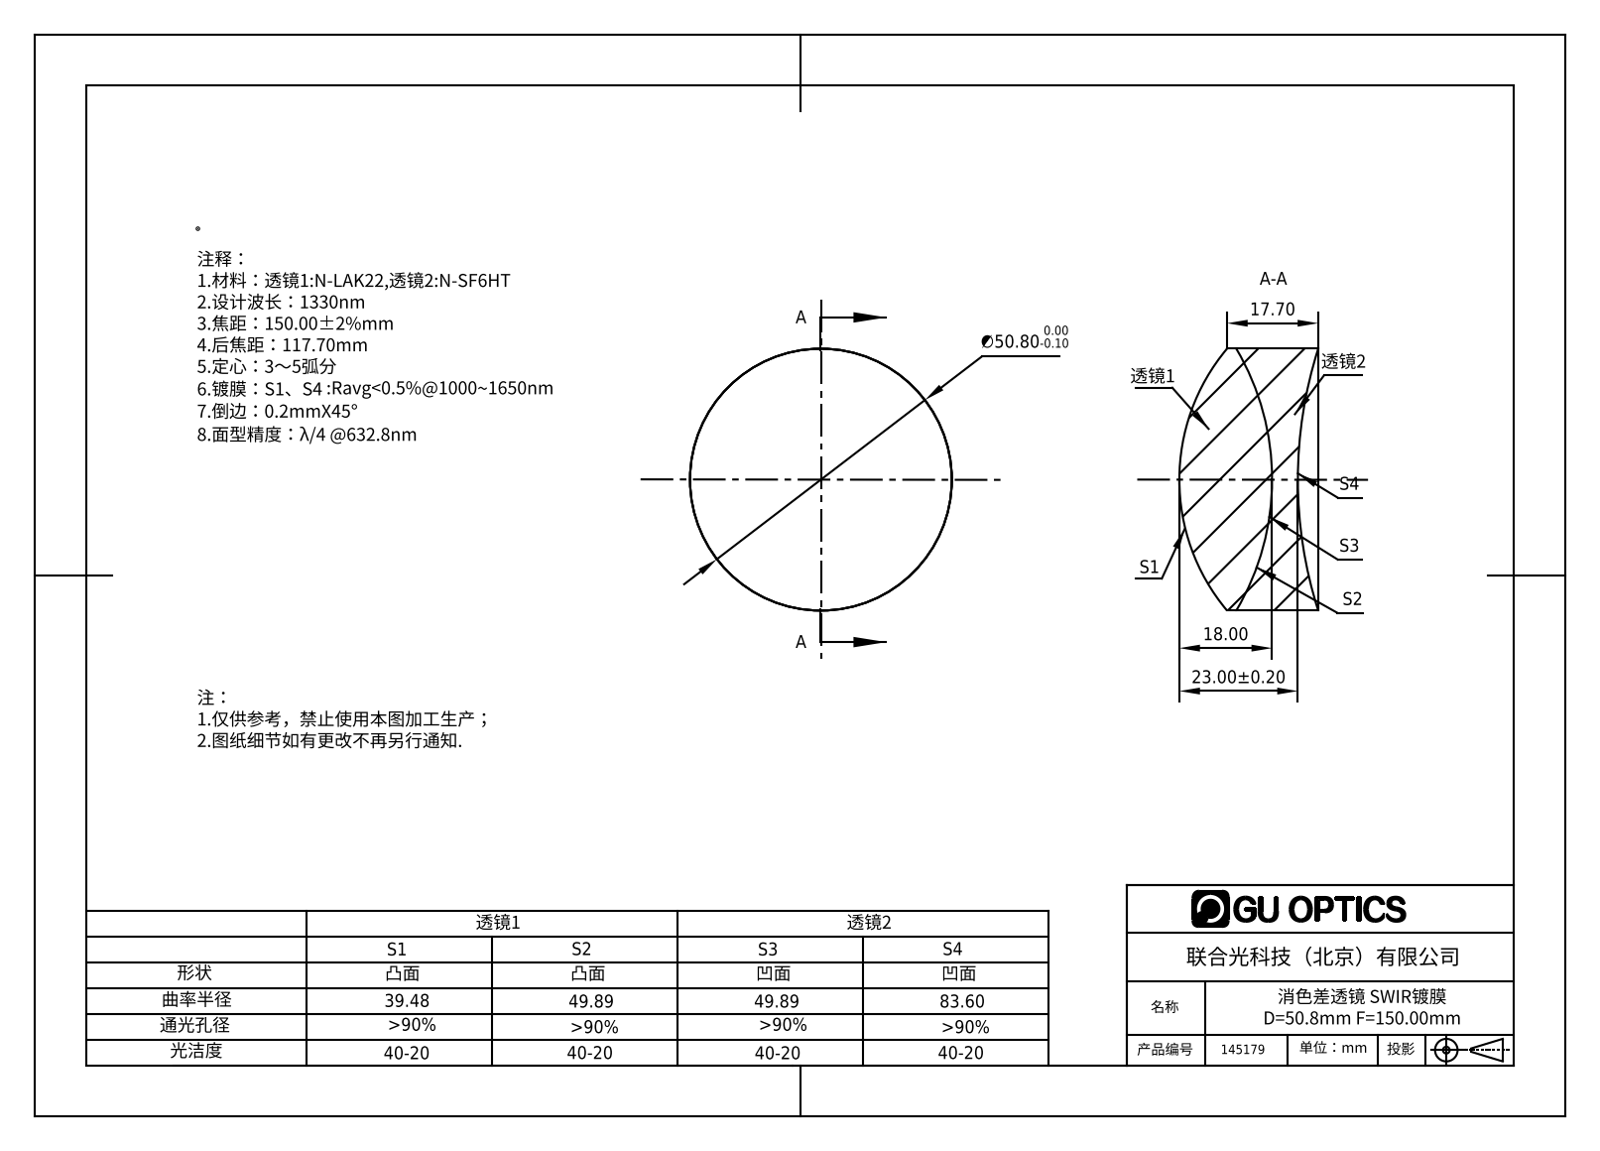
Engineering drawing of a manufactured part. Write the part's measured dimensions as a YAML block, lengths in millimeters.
part_name: "145179"
step_written_by: "SolidWorks 2016 (AUTOMOTIVE_DESIGN)"
units: millimeters
bodies: {solids: 2, faces: 12, planar: 0, cylindrical: 4, other: 8}
overall_size: [50.8, 50.8, 26.95]
volume: 41625
surface_area: 11553
round_bosses_or_shafts:
  - {diameter: 50.8, count: 1}
